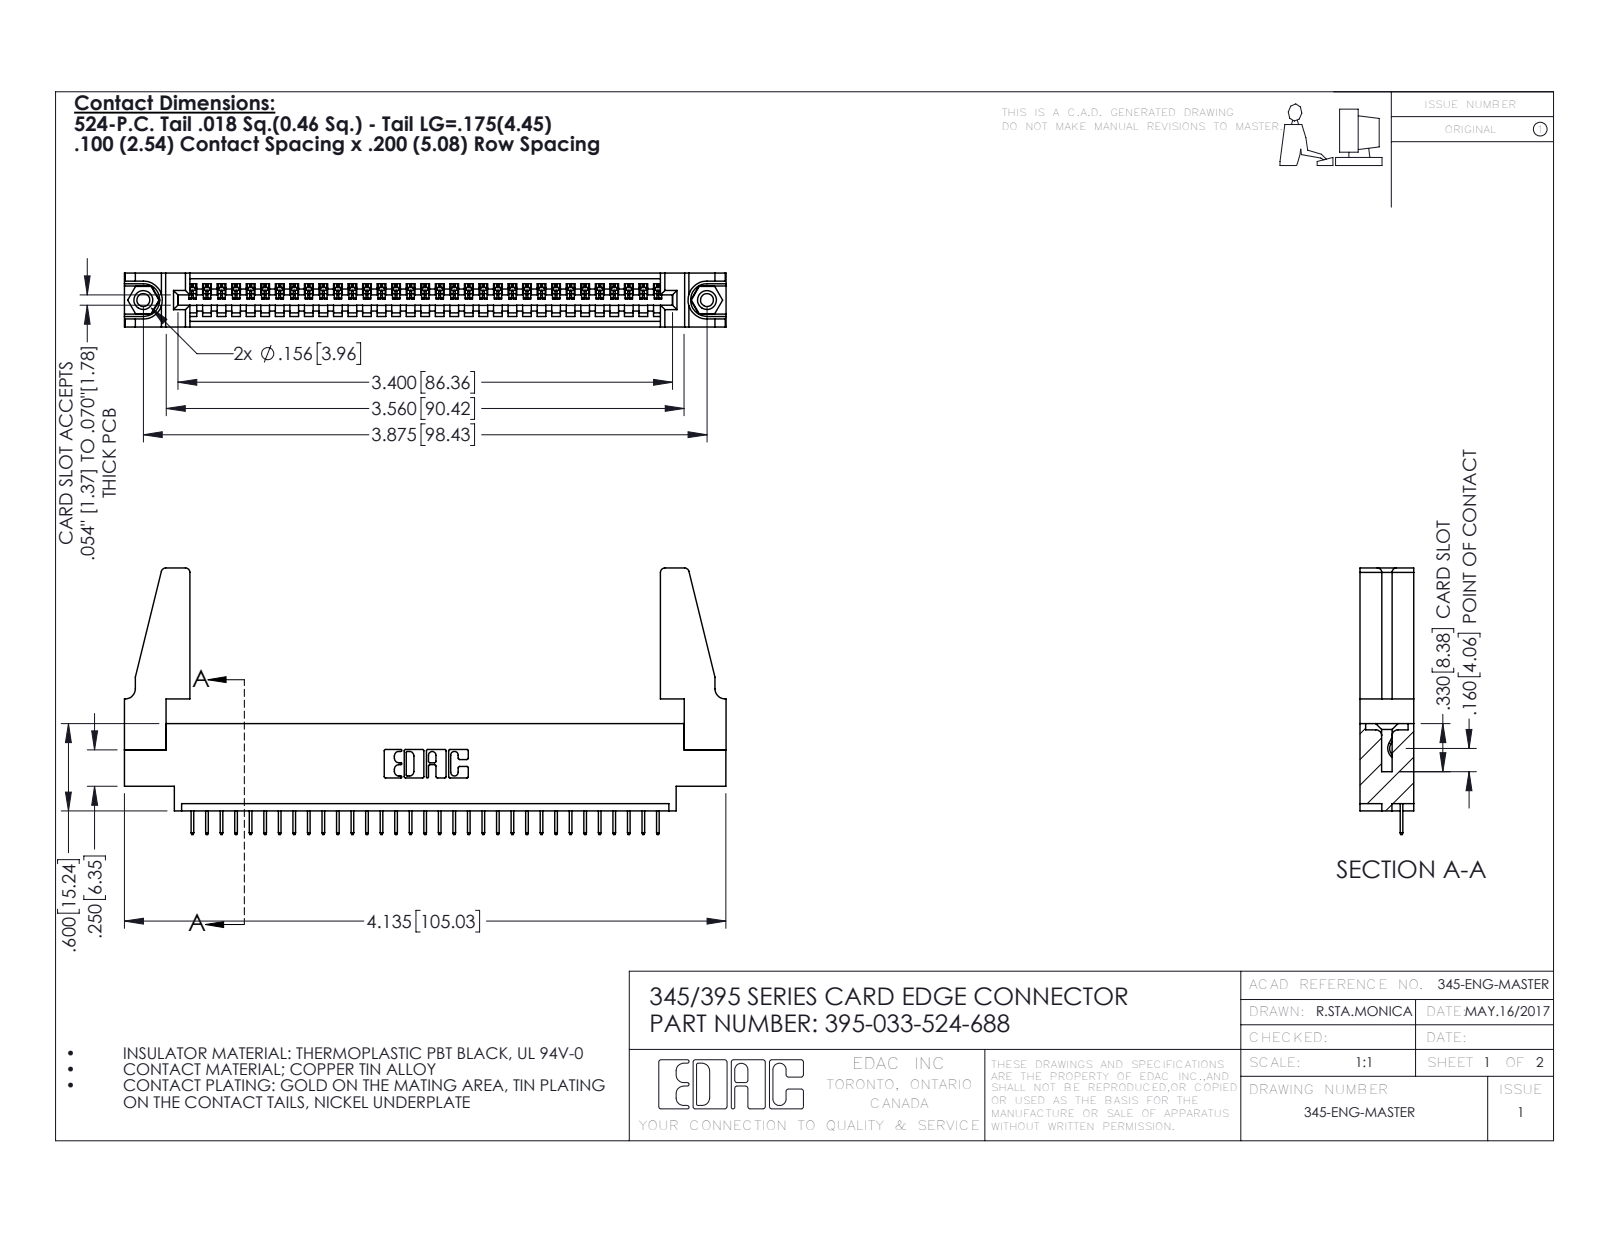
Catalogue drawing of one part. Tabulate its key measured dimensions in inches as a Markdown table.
| quantity | value |
| --- | --- |
| part name | 395-033-524-688; 345-250-001_345-250-001-102; 345 Part_0.170 Offset - 0.156 Dia-TH; 345-220-078_345-220-088 (+1 more) |
| STEP written by | SolidWorks 2016 (CONFIG_CONTROL_DESIGN) |
| units | inches |
| bodies | 38 solids, 2300 faces (1674 planar, 610 cylindrical, 16 other) |
| overall size | 4.136 × 1.832 × 0.37 |
| volume | 0.788 in³ |
| surface area | 24.11 in² |
| round holes (diameter × count) | 0.089 × 2, 0.125 × 2, 0.156 × 2, 0.064 × 1 |
| round bosses / shafts (diameter × count) | 0.155 × 2 |
| partial cylindrical surfaces (radius × count) | 0.006 × 66, 0.01 × 22, 0.03 × 8, 0.007 × 6, 0.031 × 6, 0.026 × 3, 0.031 × 2, 0.04 × 2 |
| main face-to-face distances | 0.37, 0.072, 0.298, 0.2, 0.098, 0.272, 0.025, 0.225, 0.072, 0.175 |
| hole center spacings | 0.27, 3.64, 3.875 |
